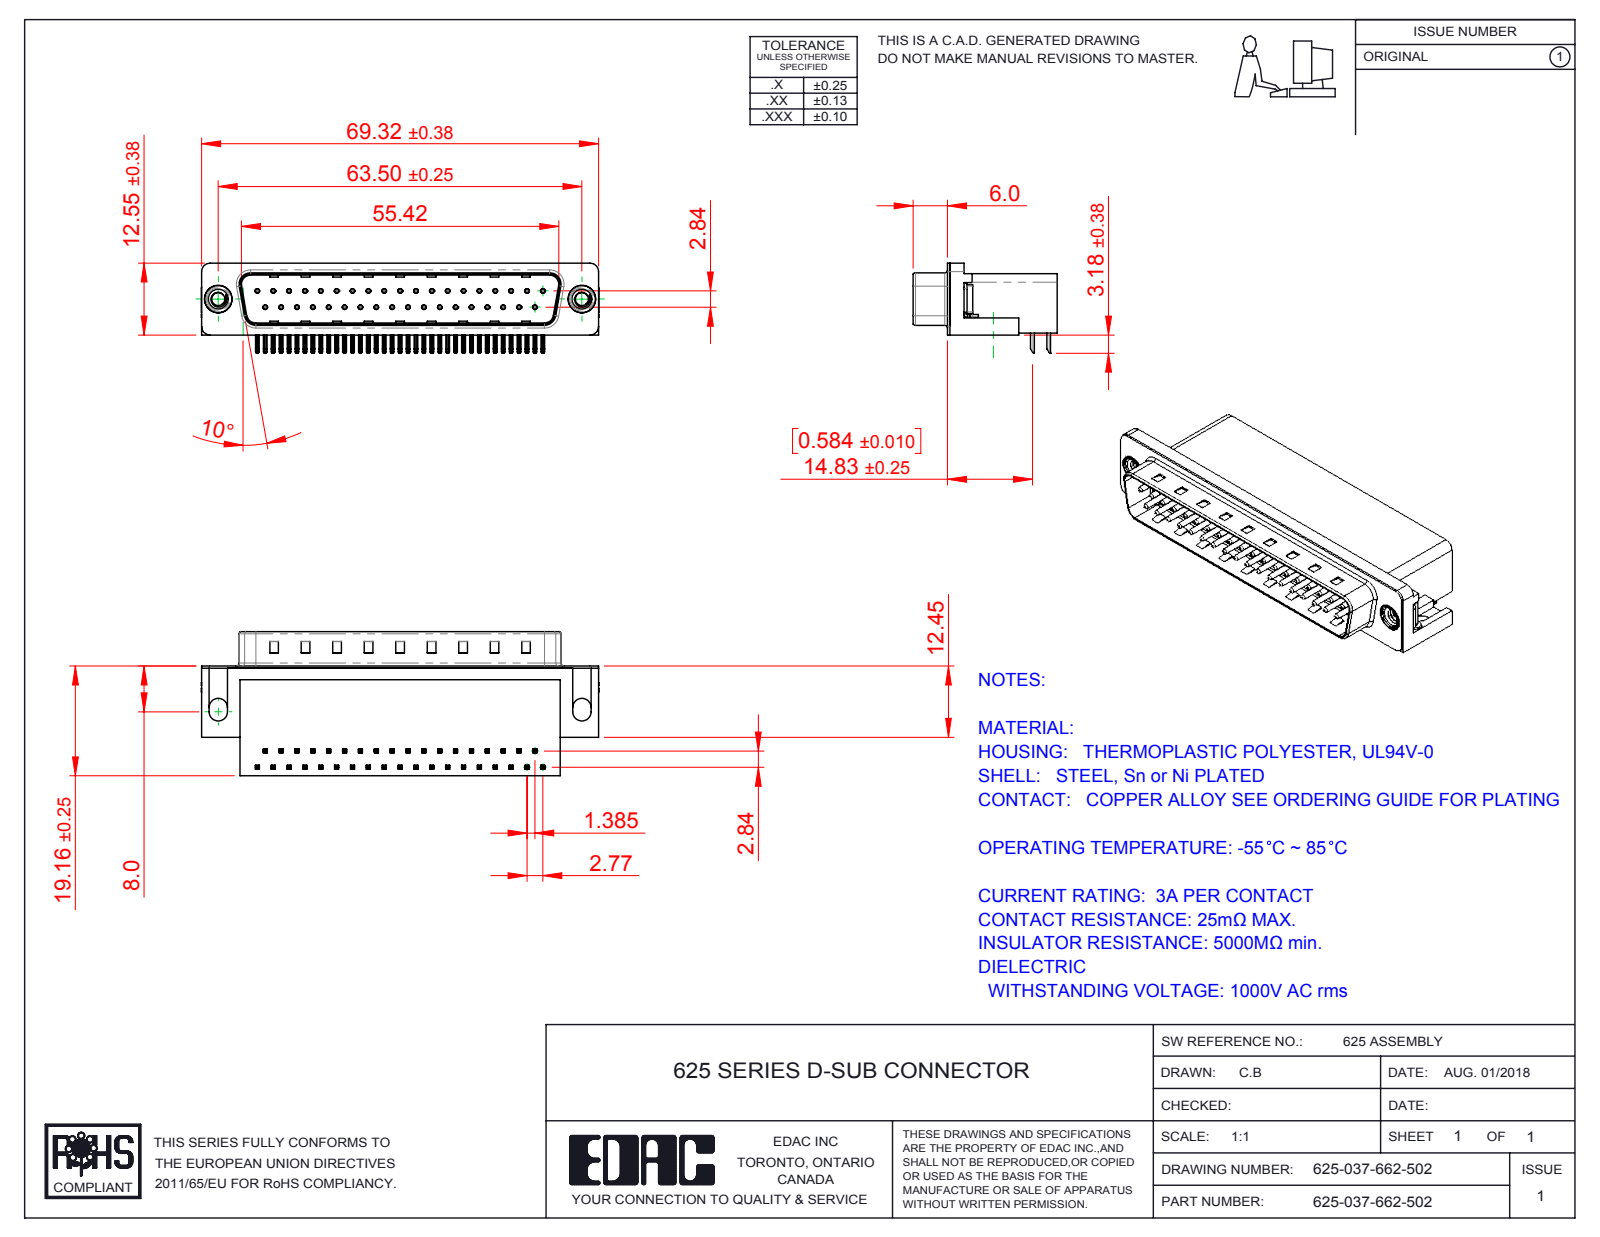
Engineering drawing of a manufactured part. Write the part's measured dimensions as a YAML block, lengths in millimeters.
part_name: "625-037-662-502; 625 Shell_37 Socket; 625 Non Board Mount; 625 Contact Bottom (+3 more)"
step_written_by: "SolidWorks 2016 (CONFIG_CONTROL_DESIGN)"
units: millimeters
bodies: {solids: 43, faces: 3199, planar: 2015, cylindrical: 913, other: 271}
overall_size: [69.4, 25.16, 15.73]
volume: 12574
surface_area: 11620
round_holes:
  - {diameter: 0.35, count: 37}
  - {diameter: 0.8, count: 37}
  - {diameter: 2.26, count: 2}
  - {diameter: 4, count: 2}
  - {diameter: 4.8, count: 2}
  - {diameter: 5, count: 2}
round_bosses_or_shafts:
  - {diameter: 0.75, count: 37}
  - {diameter: 4.9, count: 2}
  - {diameter: 4.75, count: 2}
  - {diameter: 3.9, count: 2}
partial_cylinders:
  - {radius: 0.25, count: 156}
  - {radius: 0.12, count: 74}
  - {radius: 1, count: 16}
  - {radius: 0.5, count: 9}
  - {radius: 1.6, count: 8}
  - {radius: 1.5, count: 7}
  - {radius: 0.9, count: 4}
  - {radius: 2, count: 4}
face_to_face_distances: [10.34, 0.4, 18.76, 8.76, 19.16, 2.84, 2.09, 10.1, 1.74, 8.36]
hole_center_spacings: [3.16, 2.77, 5.54, 8.31, 11.08, 13.85, 19.39, 22.16]
